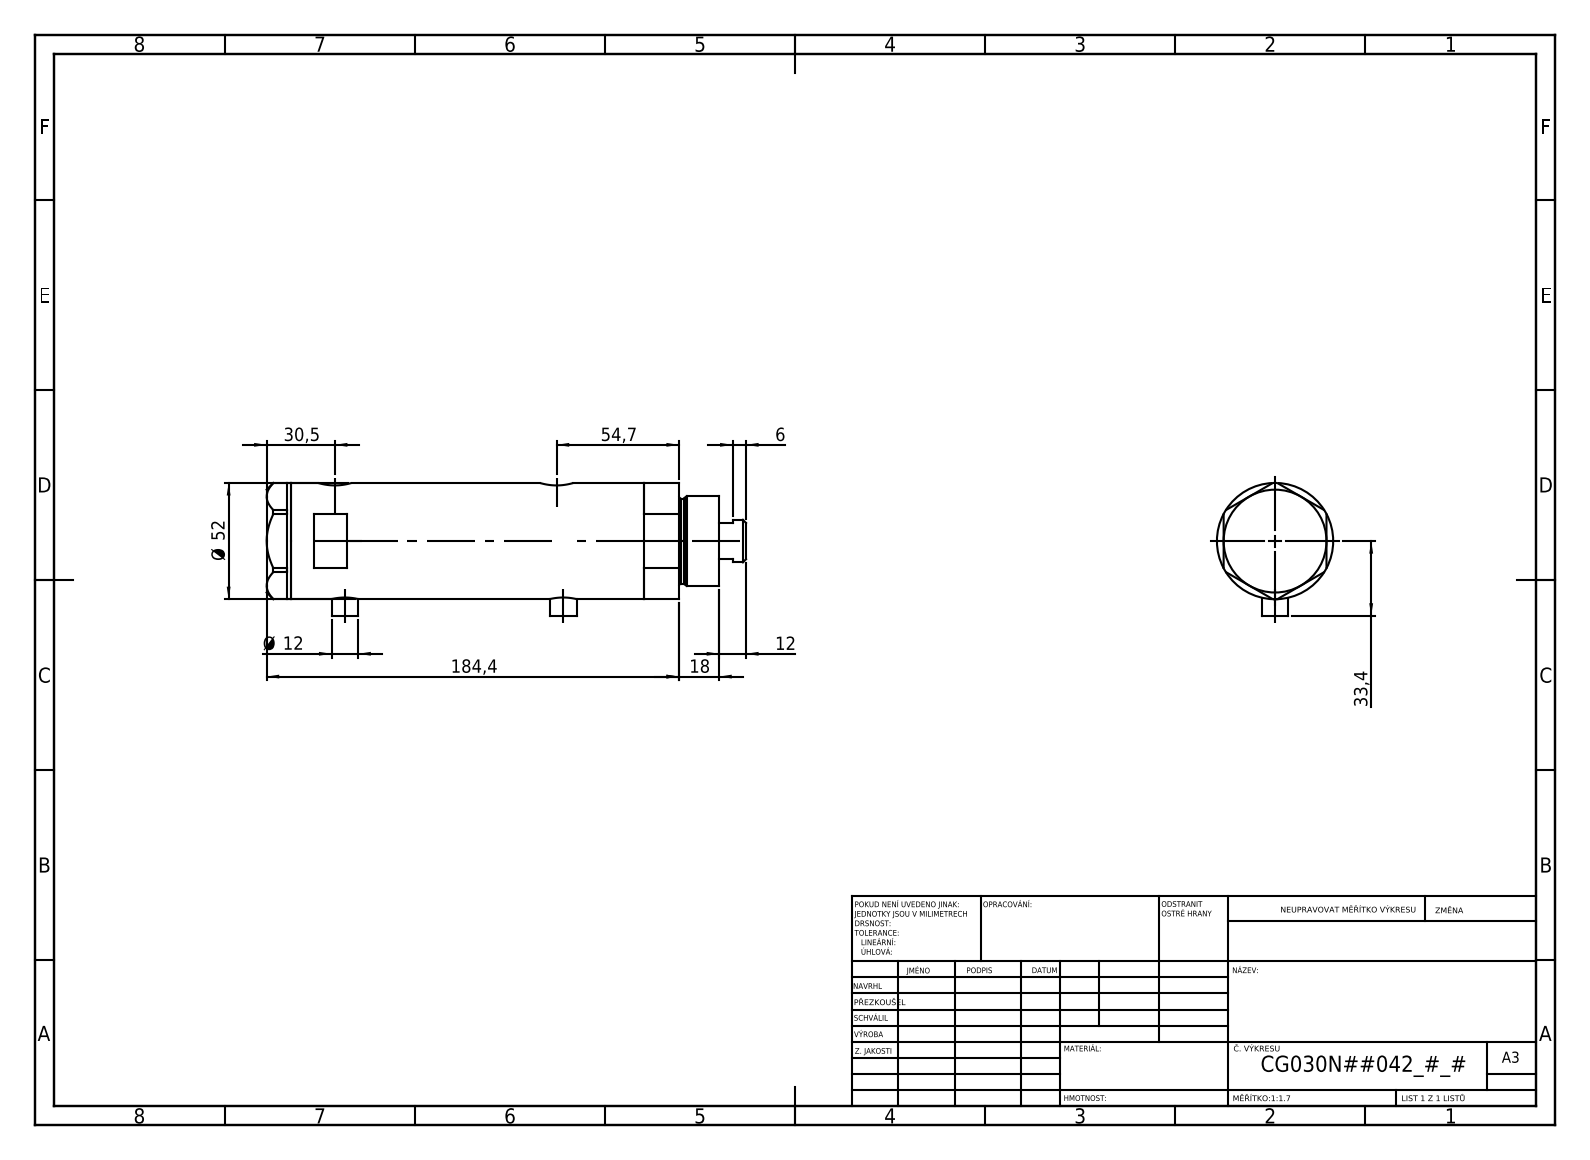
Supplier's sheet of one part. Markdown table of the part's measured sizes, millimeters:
| quantity | value |
| --- | --- |
| part name | V270CG_BACK; V270CG_VC; V270CG_FRONT; V270CG_MIDDLE |
| STEP written by | SolidWorks 2019 (CONFIG_CONTROL_DESIGN) |
| units | millimeters |
| bodies | 4 solids, 134 faces (65 planar, 49 cylindrical, 20 other) |
| overall size | 220.9 × 59.4 × 52 |
| volume | 391 702 mm³ |
| surface area | 87 014 mm² |
| round holes (diameter × count) | 9.73 × 2, 12.5 × 2, 15 × 2, 6.5 × 1, 20 × 1, 21.5 × 1, 30 × 1, 33 × 1, 44 × 1 |
| round bosses / shafts (diameter × count) | 12 × 2, 52 × 1, 40 × 1, 38 × 1, 19 × 1 |
| main face-to-face distances | 121.5, 23.8, 97.7, 11, 34.8, 132.5, 46, 168.9, 157.9, 134.1 |
| hole center spacings | 2.9, 4.5, 94.7, 97.6, 99.2, 102.1 |
